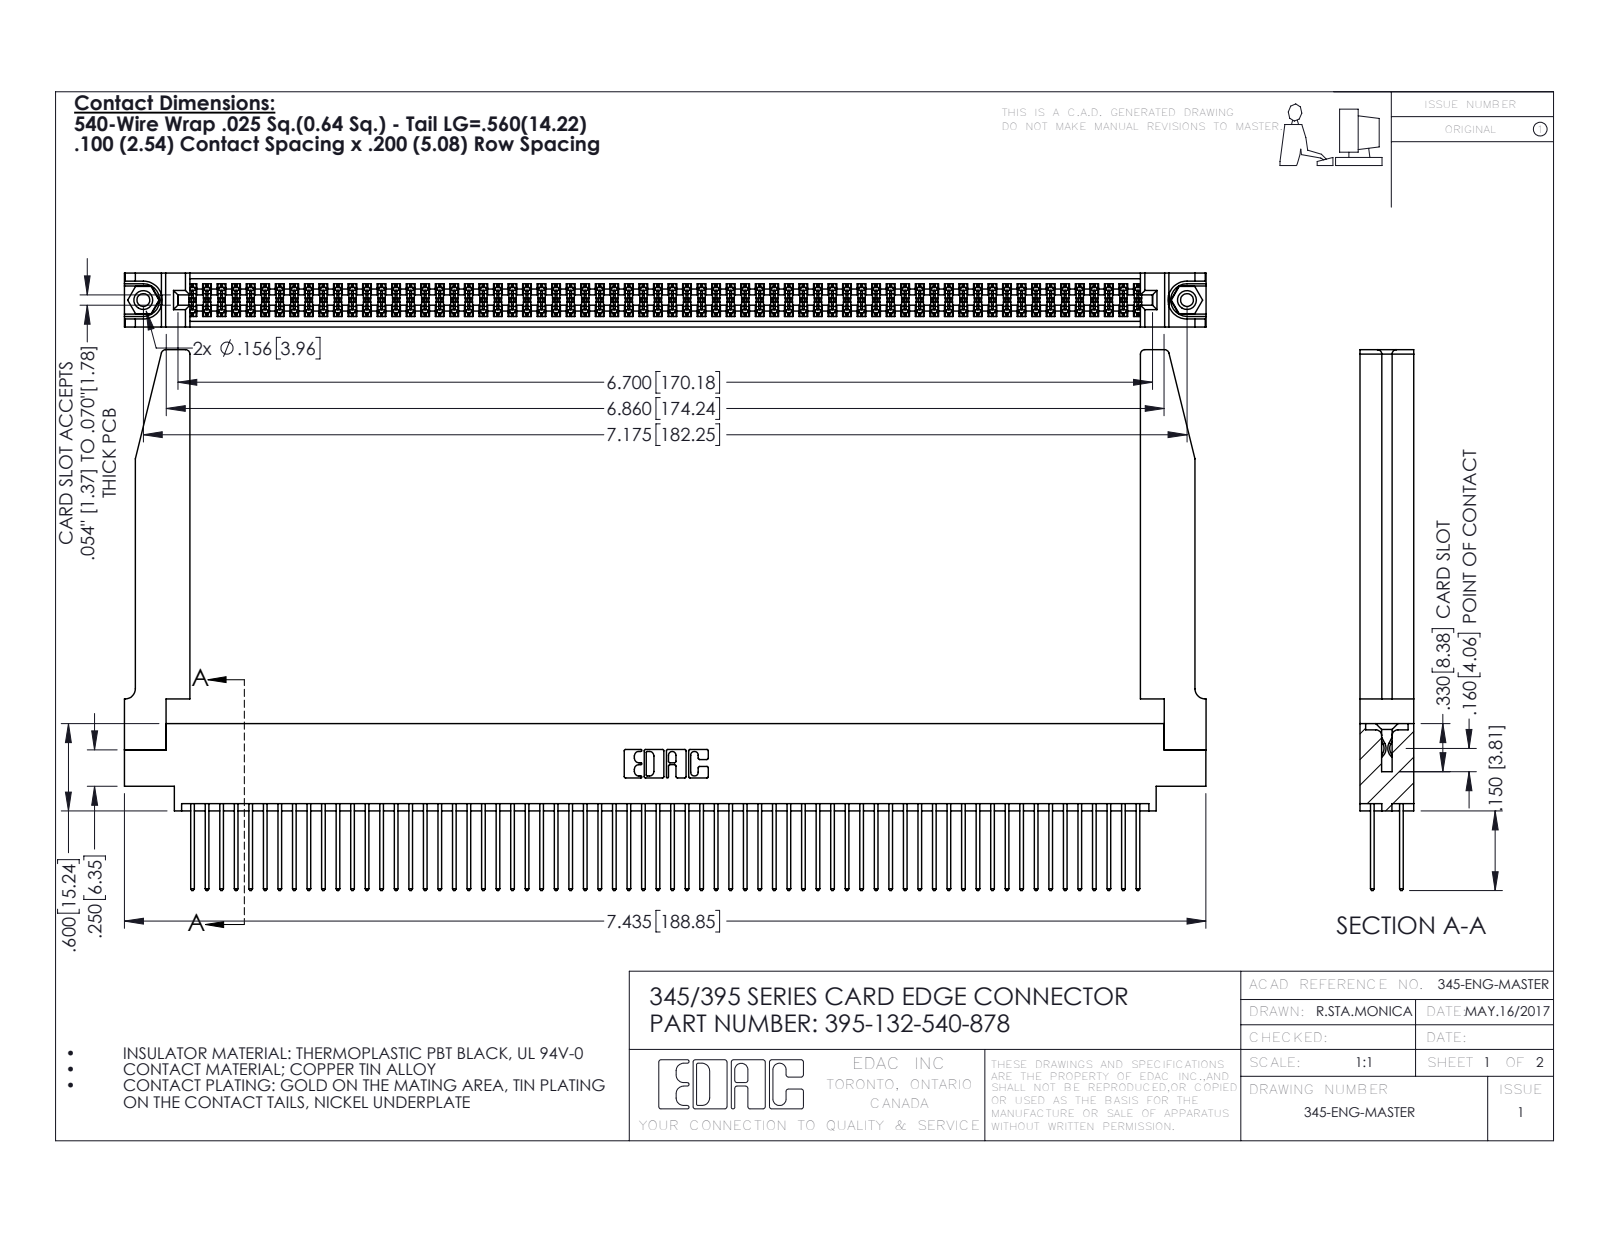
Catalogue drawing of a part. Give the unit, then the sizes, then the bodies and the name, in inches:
Units: inches
Overall size (bounding box): 7.436 × 3.717 × 0.37
Round holes (diameter × count): ⌀0.089 ×2, ⌀0.125 ×2, ⌀0.156 ×2, ⌀0.064 ×1
Round bosses / shafts (diameter × count): ⌀0.155 ×2
Partial cylindrical surfaces — rounded edges, fillets, slot ends (radius × count): R0.006 ×198, R0.01 ×132, R0.01 ×22, R0.03 ×8, R0.007 ×6, R0.031 ×6, R0.026 ×3, R0.014 ×2
Main face-to-face distances: 0.072, 0.298, 0.37, 0.098, 0.272, 0.025, 0.2, 0.225, 0.175, 0.15
Hole centre spacings: 0.27, 6.939, 7.175
Volume: 1.631 in³ · Surface area: 58.58 in²
Bodies: 137 solids, 6964 faces (4582 planar, 2330 cylindrical, 52 other)
Part name (STEP PRODUCT): 395-132-540-878; 345-220-078_345-220-078; 345-250-001_345-250-001-102; 345-292-001_345-293-140 (+1 more)
STEP written by: SolidWorks 2016 (CONFIG_CONTROL_DESIGN)
